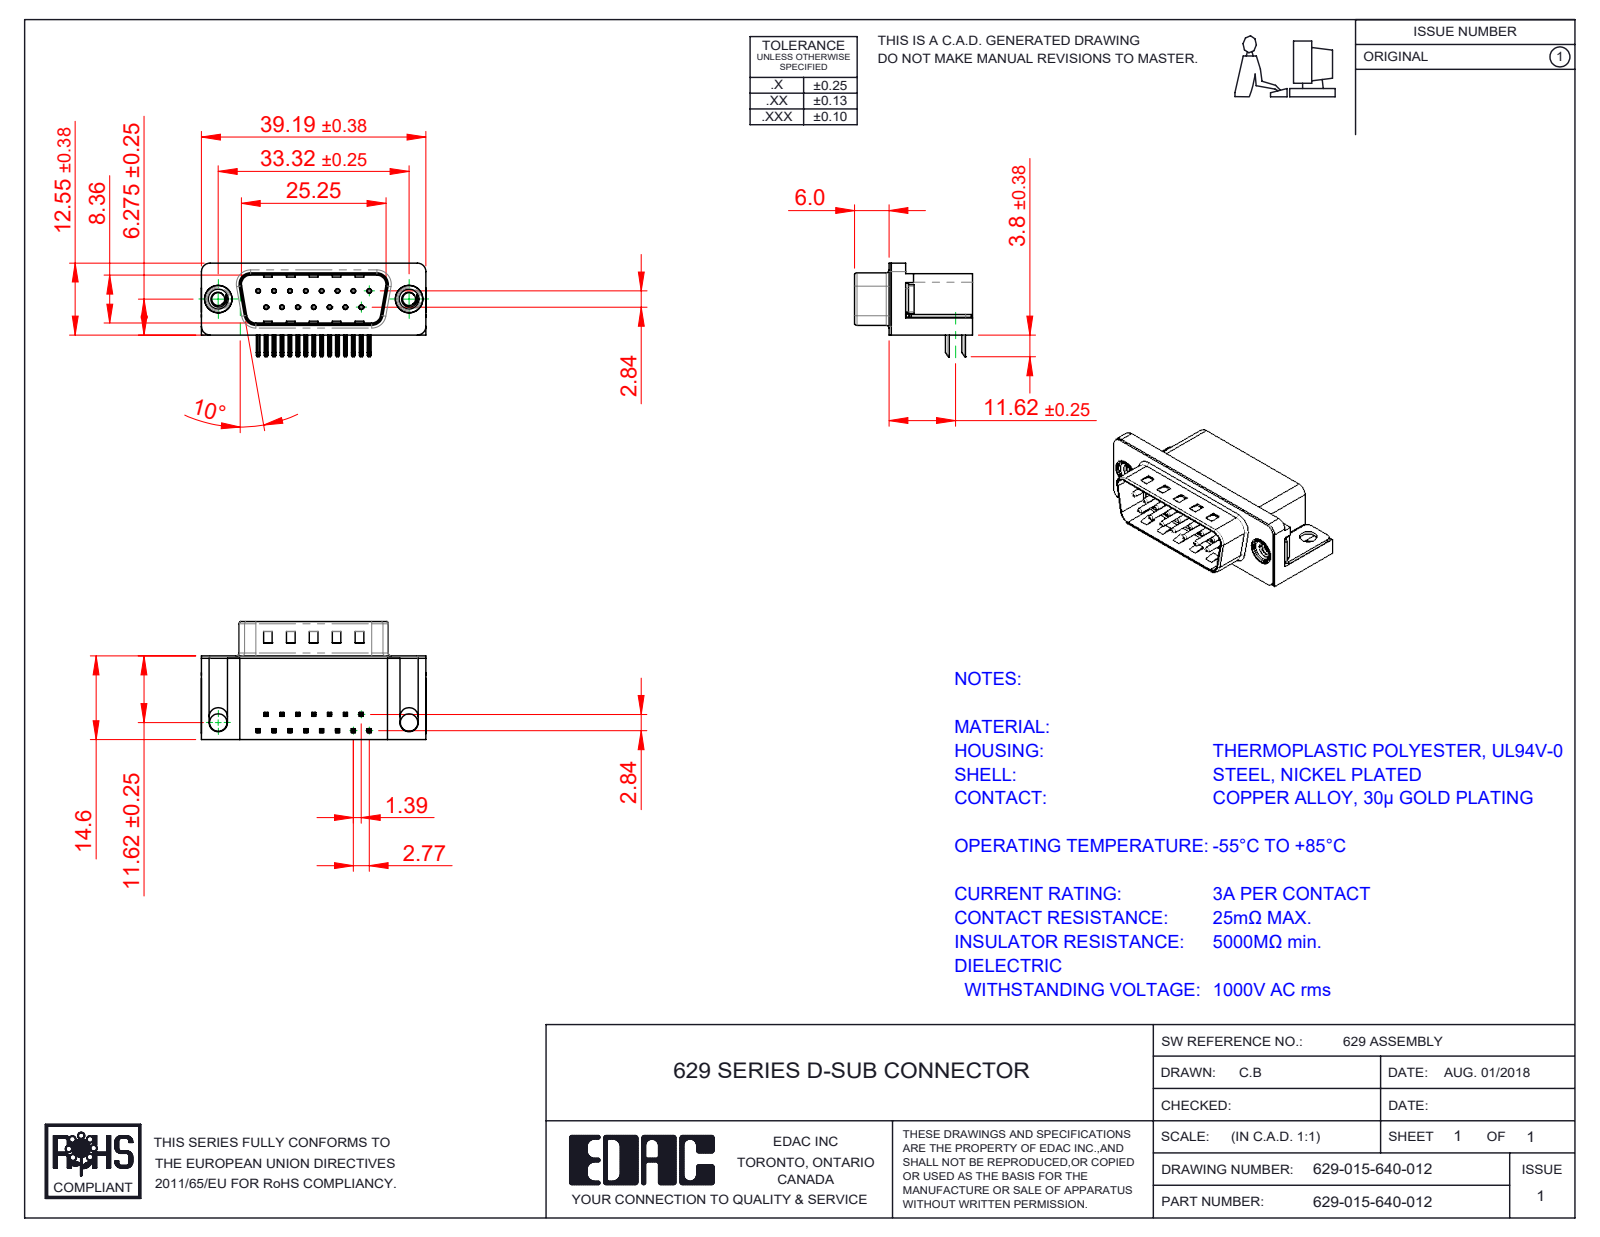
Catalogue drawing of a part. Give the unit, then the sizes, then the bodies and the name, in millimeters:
Units: millimetres
Overall size (bounding box): 39.22 × 20.6 × 16.35
Round holes (diameter × count): ⌀0.35 ×15, ⌀0.8 ×15, ⌀2.26 ×2, ⌀3.05 ×2, ⌀4 ×2, ⌀4.8 ×2, ⌀5 ×2
Round bosses / shafts (diameter × count): ⌀0.75 ×15, ⌀4.9 ×2, ⌀4.75 ×2, ⌀3.9 ×2
Partial cylindrical surfaces — rounded edges, fillets, slot ends (radius × count): R0.25 ×68, R0.12 ×30, R1 ×16, R0.5 ×9, R1.6 ×8, R1.5 ×6, R0.9 ×4, R2 ×4
Main face-to-face distances: 0.4, 14.2, 10.35, 2.1, 14.6, 10.46, 1.7, 10.86, 8.76, 0.5
Hole centre spacings: 3.16, 2.77, 5.54, 8.31, 11.08, 5.03, 5.04, 7.48
Volume: 5 077 mm³ · Surface area: 6 041 mm²
Bodies: 21 solids, 1475 faces (891 planar, 445 cylindrical, 139 other)
Part name (STEP PRODUCT): 629 Contact Top; 629 4-40 Threaded Rivet; 629 Thru Hole Board Mount; 629-015-640-012 (+3 more)
STEP written by: SolidWorks 2020 (CONFIG_CONTROL_DESIGN)
